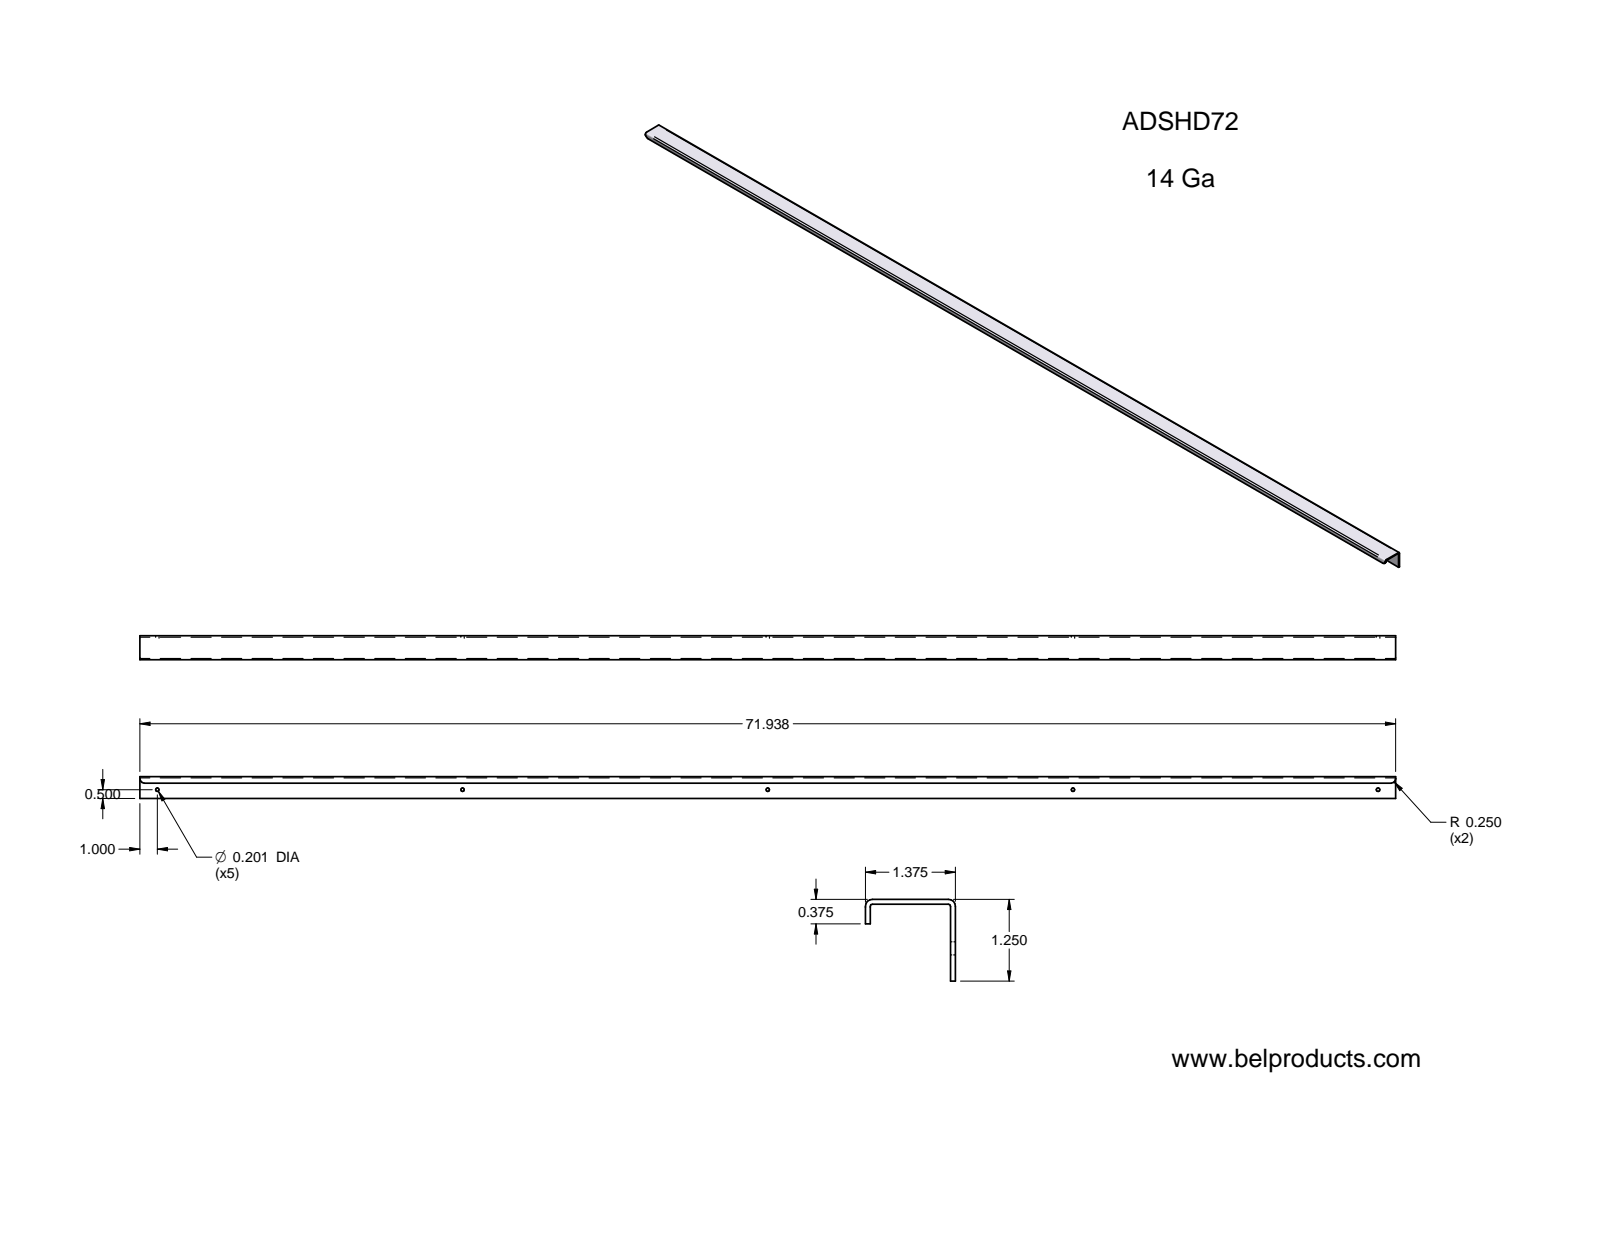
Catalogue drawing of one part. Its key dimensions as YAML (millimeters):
step_written_by: "Unknown (AUTOMOTIVE_DESIGN)"
units: millimeters
bodies: {solids: 1, faces: 21, planar: 10, cylindrical: 11, other: 0}
overall_size: [1827.21, 34.92, 31.75]
volume: 246475
surface_area: 266141
round_holes:
  - {diameter: 5.11, count: 5}
partial_cylinders:
  - {radius: 0.81, count: 2}
  - {radius: 2.72, count: 2}
  - {radius: 6.35, count: 2}
face_to_face_distances: [1.9, 1.91, 33.02, 34.92, 31.12, 29.85, 31.76, 22.23, 7.62, 9.53]
hole_center_spacings: [444.1, 444.11, 888.21, 1332.31, 888.2, 1776.42]
